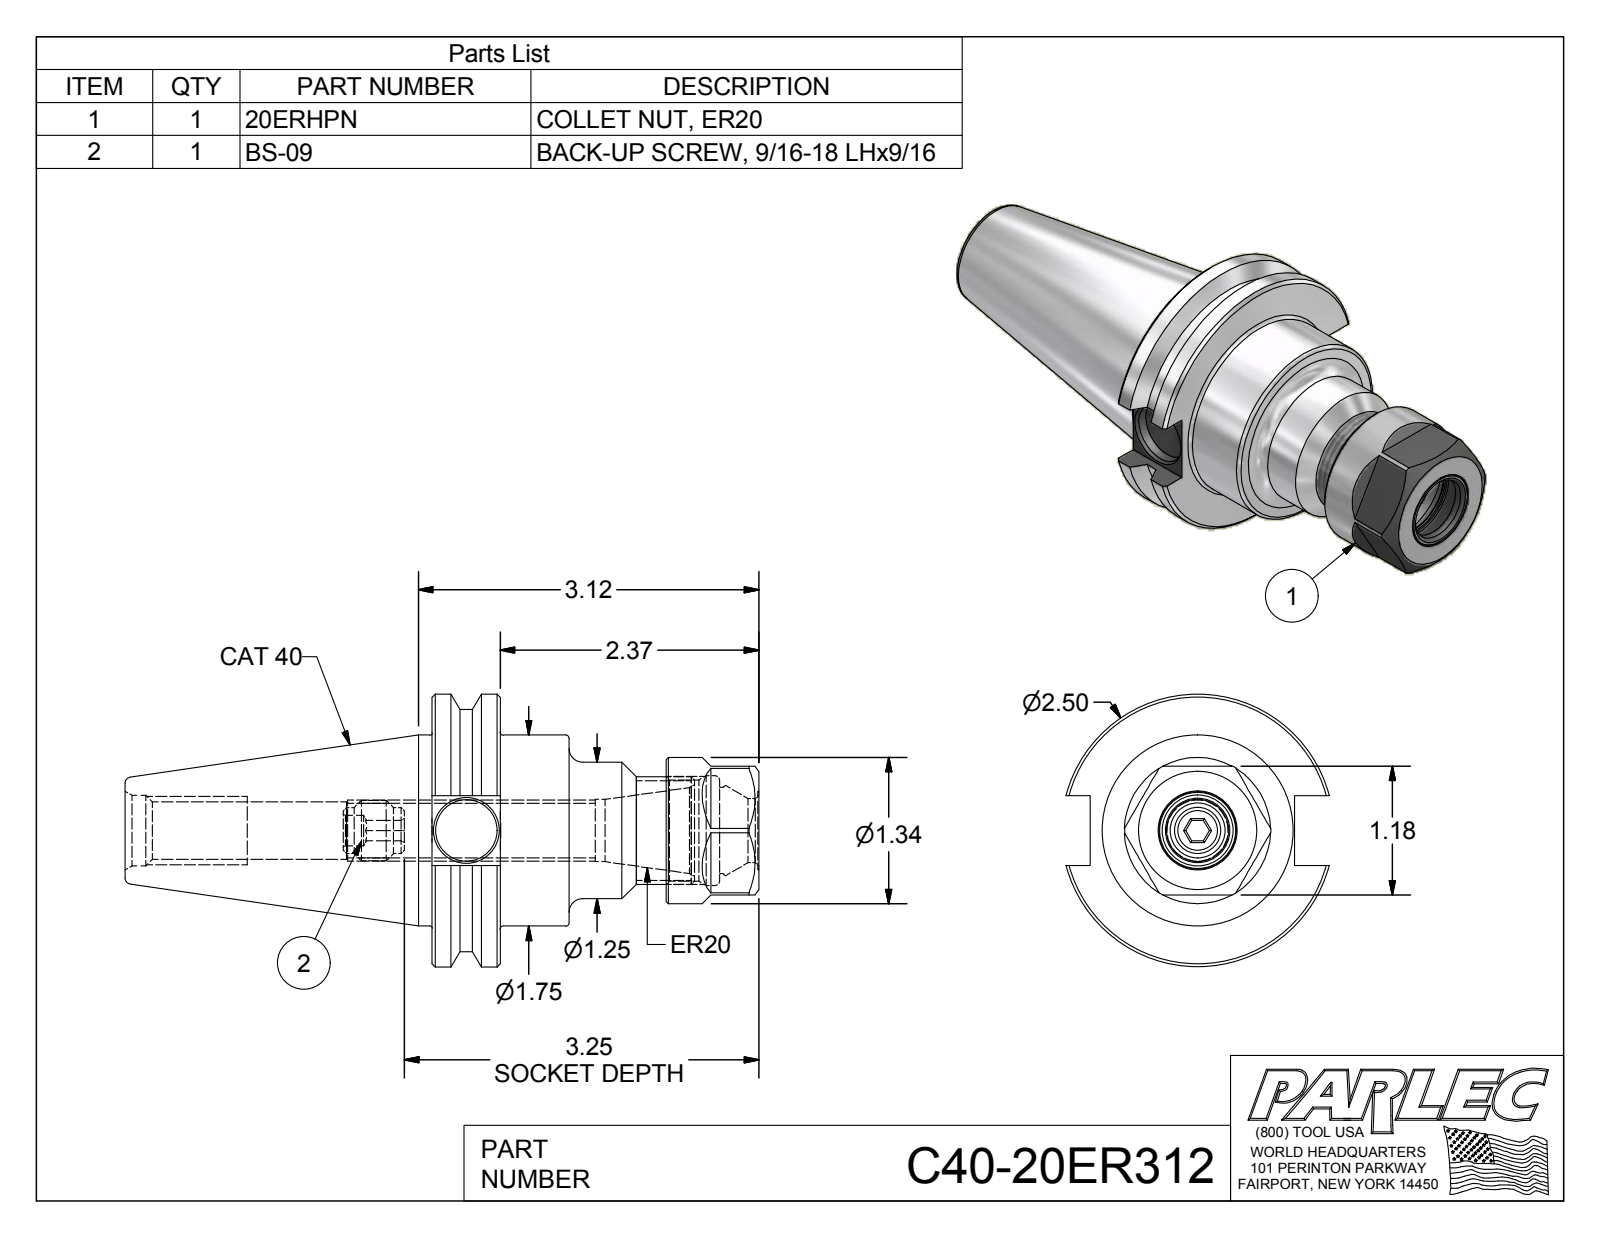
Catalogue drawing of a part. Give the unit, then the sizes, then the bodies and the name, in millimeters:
Units: millimetres
Overall size (bounding box): 147.5 × 63.5 × 61.4
Round holes (diameter × count): ⌀7.1 ×1, ⌀12.8 ×1, ⌀13.4 ×1, ⌀14.3 ×1, ⌀14.5 ×1, ⌀14.9 ×1, ⌀16.5 ×1, ⌀20.1 ×1, ⌀23.5 ×1, ⌀25.5 ×1
Round bosses / shafts (diameter × count): ⌀63.5 ×1, ⌀56.4 ×1, ⌀44.5 ×1, ⌀34 ×1, ⌀31.8 ×1, ⌀25 ×1, ⌀14.1 ×1, ⌀10.7 ×1
Main face-to-face distances: 15.9, 30, 54.5, 38.6, 76.1, 60.2, 21.6, 6.9, 23.1, 31.9
Volume: 147 700 mm³ · Surface area: 32 190 mm²
Bodies: 3 solids, 107 faces (42 planar, 24 cylindrical, 41 other)
Part name (STEP PRODUCT): C40-20ER312; C40-20ER3-1; 20ERHPN; BS-09
STEP written by: Autodesk Inventor 2012 (AUTOMOTIVE_DESIGN)
